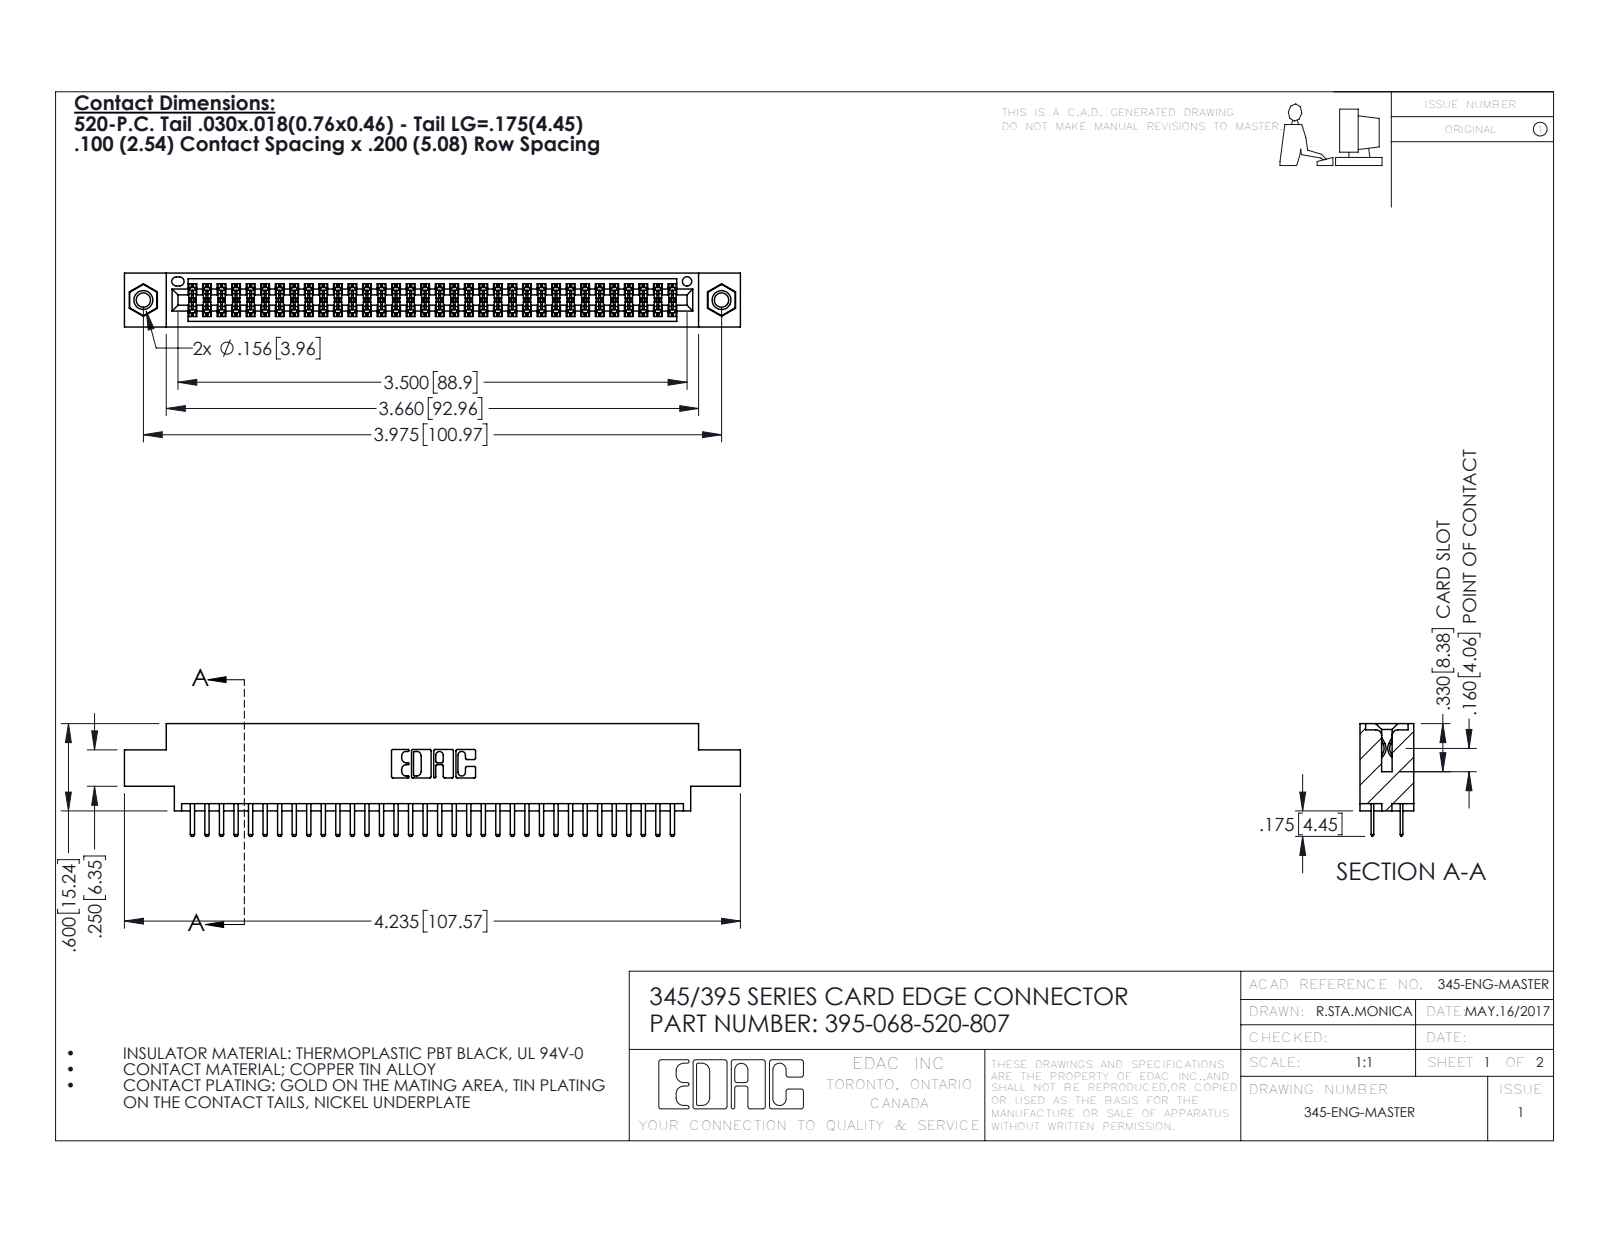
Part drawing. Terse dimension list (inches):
name: 345 Part_0.170 Offset - 0.156 Dia-TI; 345-250-001_345-250-005-103; 395-068-520-807; 345-292-001_345-293-120
written by: SolidWorks 2016 (CONFIG_CONTROL_DESIGN)
unit: in
bodies: 71 solids, 3862 faces (2496 planar, 1350 cylindrical, 16 other)
size: 4.235 × 0.775 × 0.37
volume: 0.624 in³; area: 23.34 in²
holes: 2× ⌀0.098, 2× ⌀0.125, 2× ⌀0.156, 1× ⌀0.064
bosses: 2× ⌀0.155
rounds: 102× R0.006, 72× R0.01, 22× R0.01, 6× R0.007, 6× R0.031, 3× R0.026, 2× R0.014, 2× R0.019
face distances: 0.072, 0.298, 0.2, 0.37, 0.098, 0.272, 0.025, 0.225, 0.022, 0.175
hole spacings: 0.27, 3.74, 3.975
